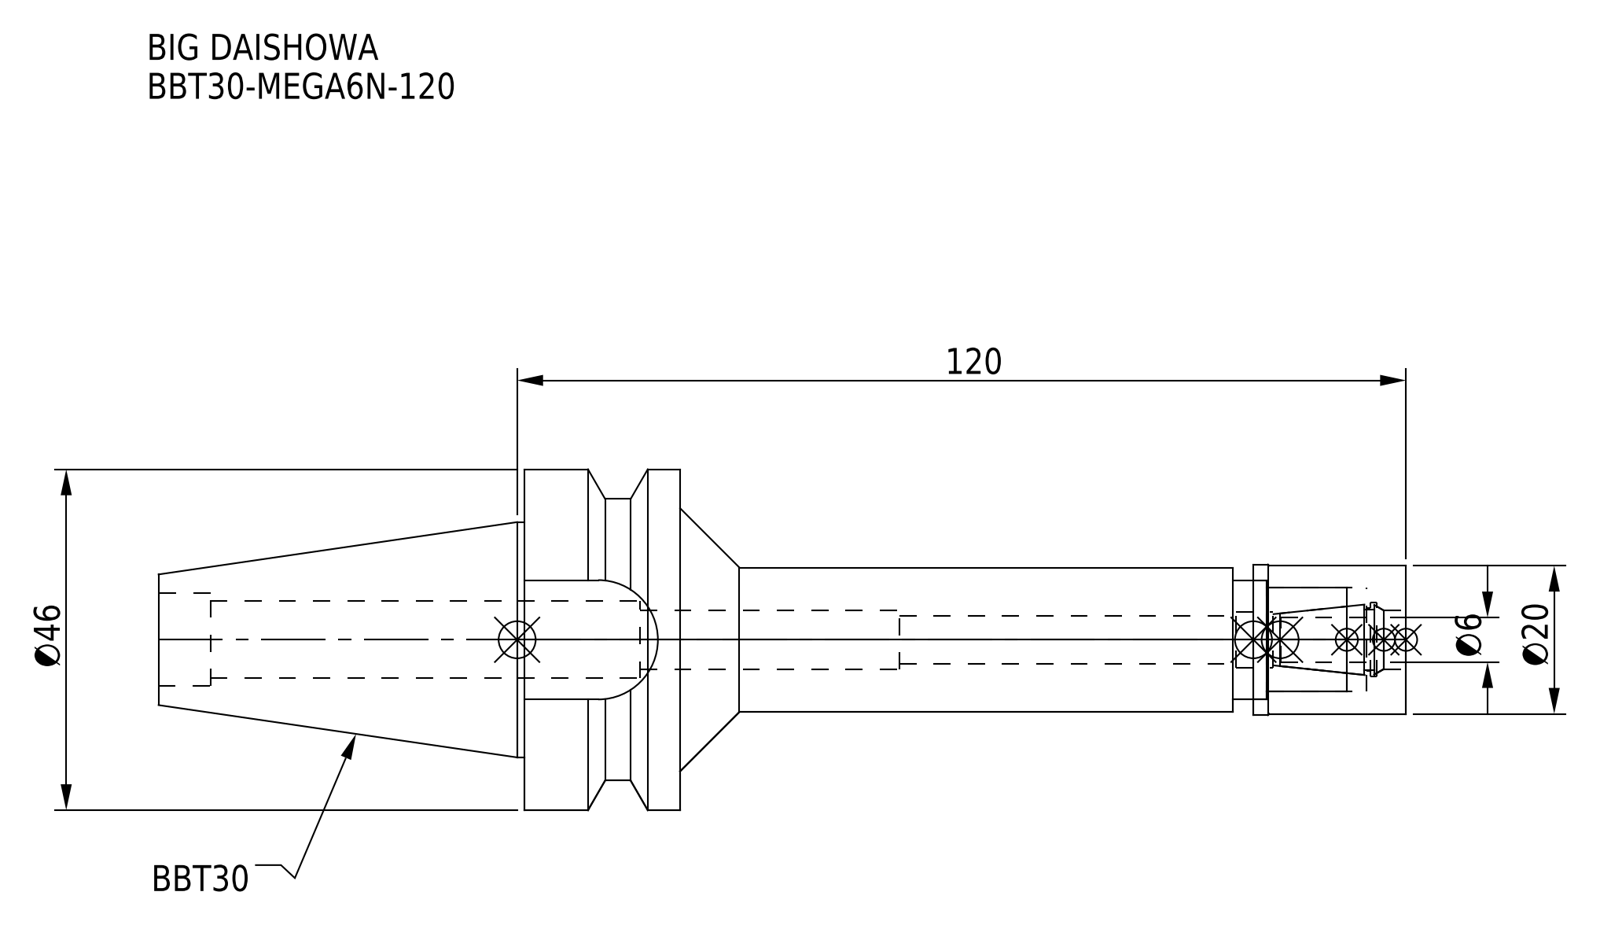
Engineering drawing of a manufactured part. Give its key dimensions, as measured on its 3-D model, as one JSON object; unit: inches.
{"part_name": "BBT30-MEGA6N-120-060-FreeParts; BBT30-MEGA6N-120-060.stp; BBT30-MEGA6N-120; BBT30-MEGA6N-120_1.stp (+3 more)", "step_written_by": "SolidWorks 2019 (CONFIG_CONTROL_DESIGN)", "units": "inches", "bodies": {"solids": 2, "faces": 79, "planar": 23, "cylindrical": 42, "other": 14}, "overall_size": [6.63, 1.811, 1.811], "volume_in3": 4.59, "surface_area_in2": 34.49, "round_holes": [[0.252, 1], [0.295, 1], [0.311, 1], [0.315, 1], [0.335, 1], [0.394, 1], [0.409, 1], [0.492, 1], [0.551, 1], [0.63, 1]], "round_bosses_or_shafts": [[1.811, 1], [1.25, 1], [0.799, 1], [0.787, 1], [0.768, 1]], "partial_cylinders_radius": [[0.317, 1], [0.748, 1]], "face_to_face_distances": [0.827, 3.858, 4.685, 1.283, 0.811, 3.047, 3.874, 6.63, 5.819, 2.772]}
